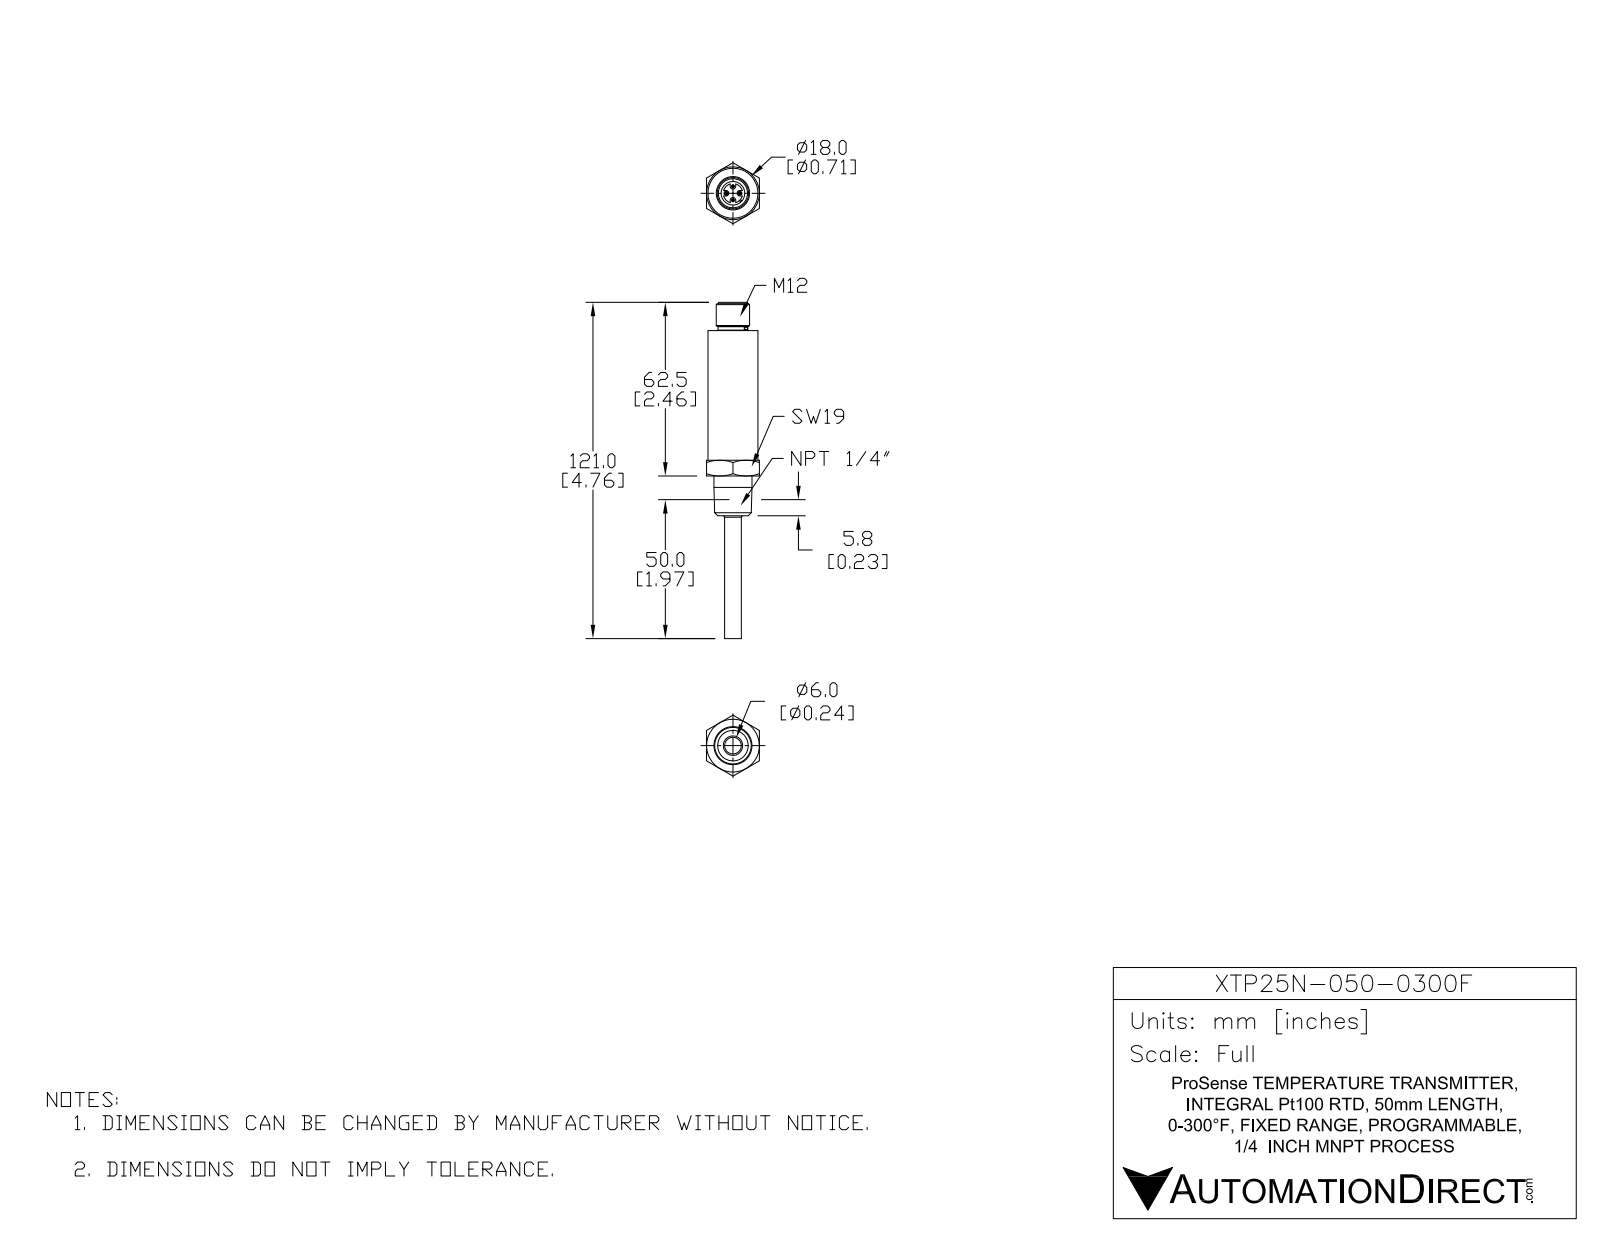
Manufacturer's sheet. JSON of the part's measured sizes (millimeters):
{"part_name": "XTP25N-050-0300F", "step_written_by": "SolidWorks 2015 (AUTOMOTIVE_DESIGN)", "units": "millimeters", "bodies": {"solids": 1, "faces": 117, "planar": 43, "cylindrical": 34, "other": 40}, "overall_size": [121, 21.94, 19], "volume_mm3": 17233, "surface_area_mm2": 6004, "round_holes": [[4, 1], [8.5, 1]], "round_bosses_or_shafts": [[1.02, 4], [18, 1], [13.72, 1], [12, 1], [10.7, 1], [10.5, 1], [6, 1]], "partial_cylinders_radius": [[1, 4], [3.5, 1], [4.25, 1]], "face_to_face_distances": [19, 52.3, 14.3, 66.6, 20, 5.7, 46.6, 76.8, 62.5, 56.8]}
